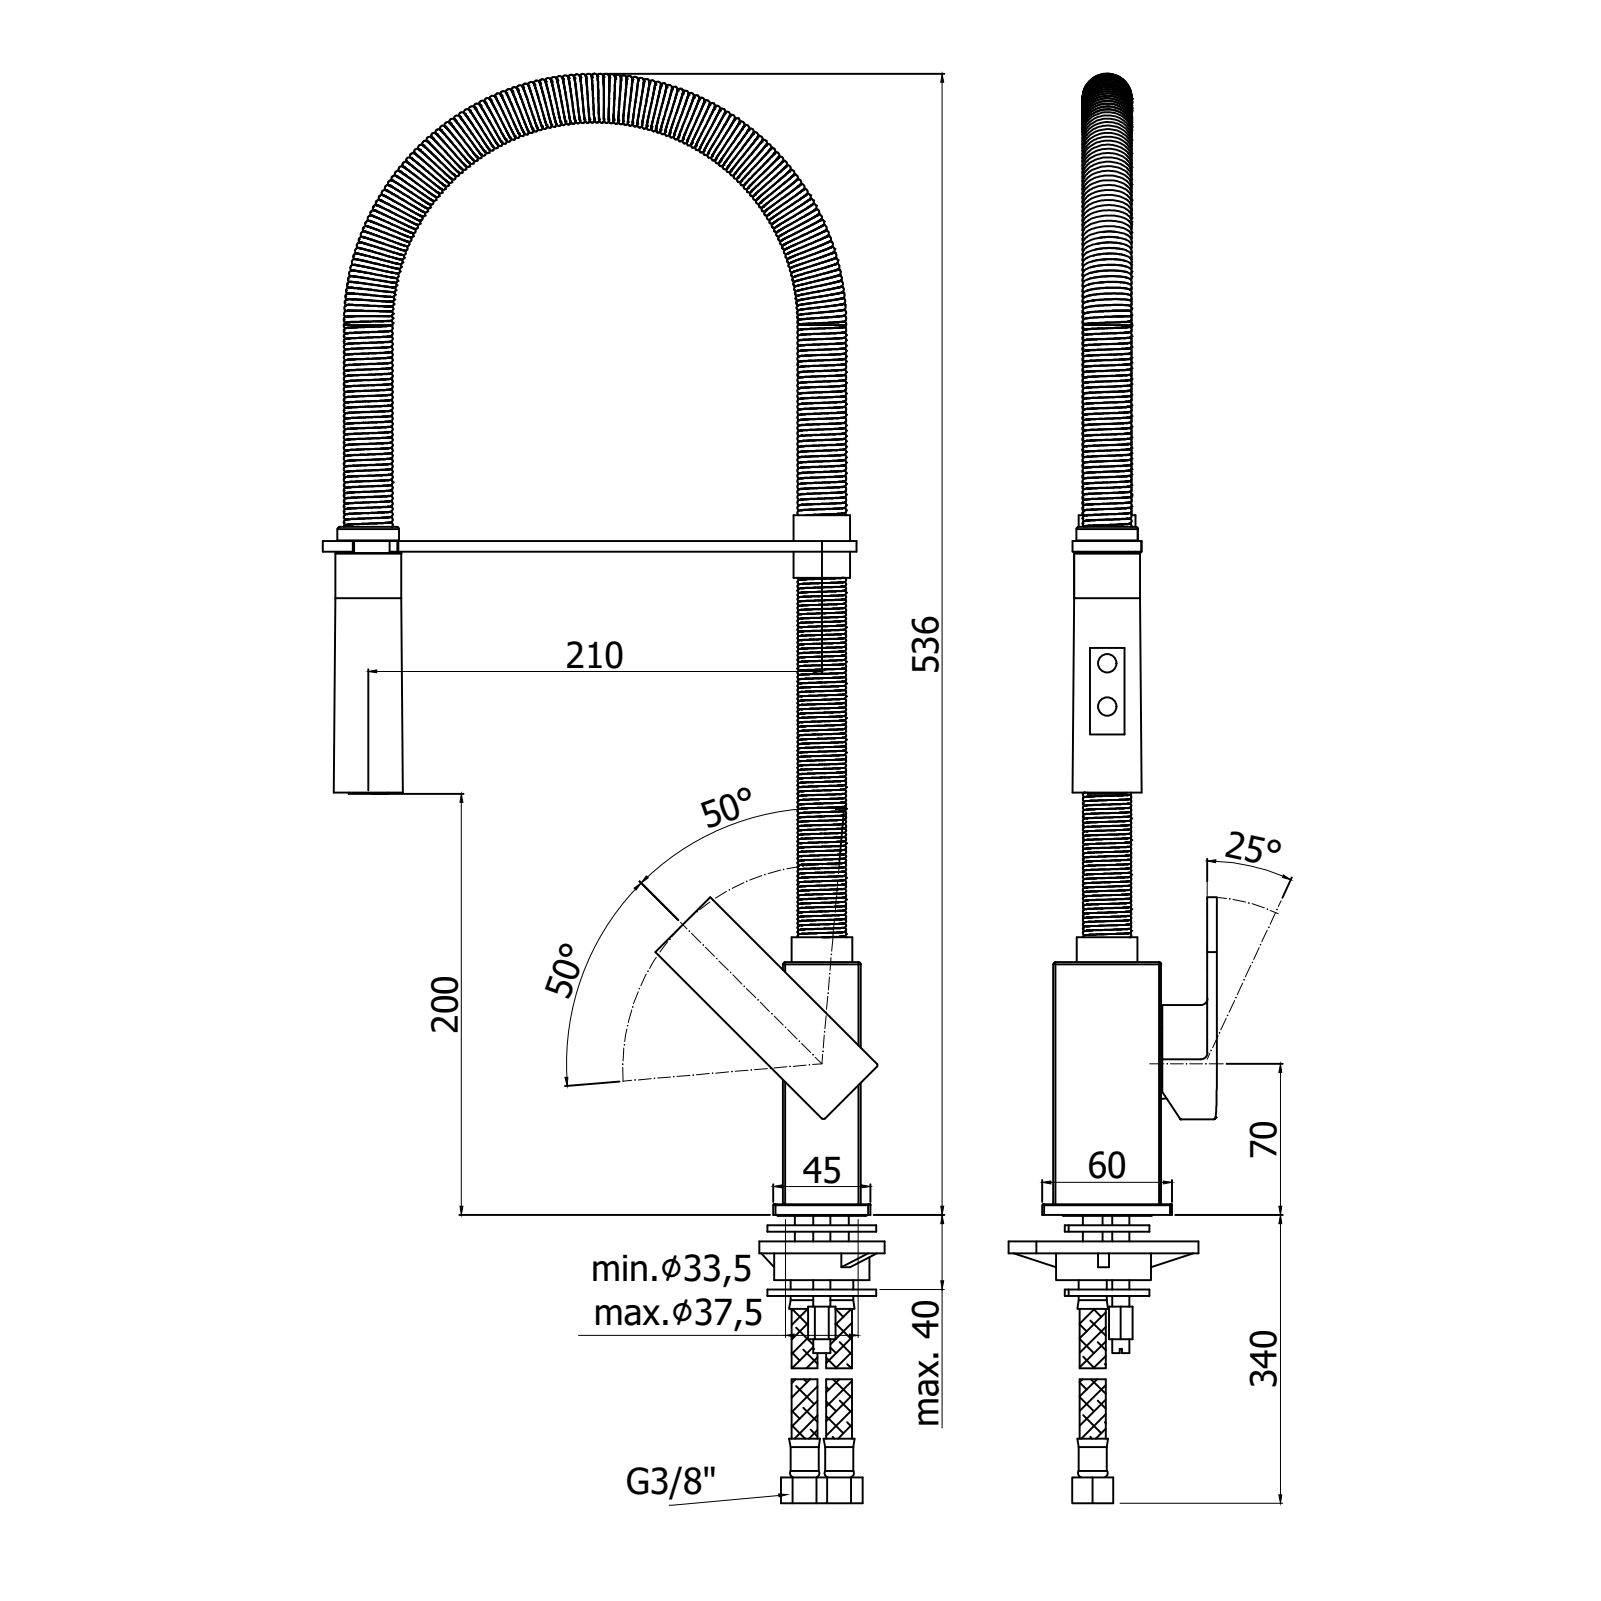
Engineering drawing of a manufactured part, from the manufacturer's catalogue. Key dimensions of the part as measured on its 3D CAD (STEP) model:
Part name (STEP PRODUCT): EL179CR
STEP written by: CREO PARAMETRIC BY PTC INC, 2020044 (CONFIG_CONTROL_DESIGN)
Units: millimetres
Bodies: 4 solids, 2709 faces (930 planar, 1005 cylindrical, 774 other)
Overall size (bounding box): 535.57 × 256.24 × 83.28
Volume: 361 316 mm³ · Surface area: 254 775 mm²
Round holes (diameter × count): ⌀0.5 ×172, ⌀5 ×2, ⌀5.5 ×2, ⌀6 ×2, ⌀9 ×2, ⌀9.9 ×2, ⌀11 ×2, ⌀23 ×2, ⌀3 ×1, ⌀3.3 ×1, ⌀4.5 ×1, ⌀5.2 ×1
Round bosses / shafts (diameter × count): ⌀0.7 ×16, ⌀9.5 ×2, ⌀4 ×2, ⌀38.8 ×1, ⌀34 ×1, ⌀30.5 ×1, ⌀28.75 ×1, ⌀28.5 ×1
Partial cylindrical surfaces — rounded edges, fillets, slot ends (radius × count): R0.5 ×75, R1 ×43, R0.25 ×34, R0.3 ×23, R0.7 ×10, R0.2 ×9, R1.5 ×8, R0.8 ×6
Main face-to-face distances: 5, 36, 78.28, 28.28, 50, 4, 74.28, 24.28, 9, 310
Hole centre spacings: 7.87, 0.69, 0.7, 1.39, 5.02, 5.53, 7.1, 7.23
